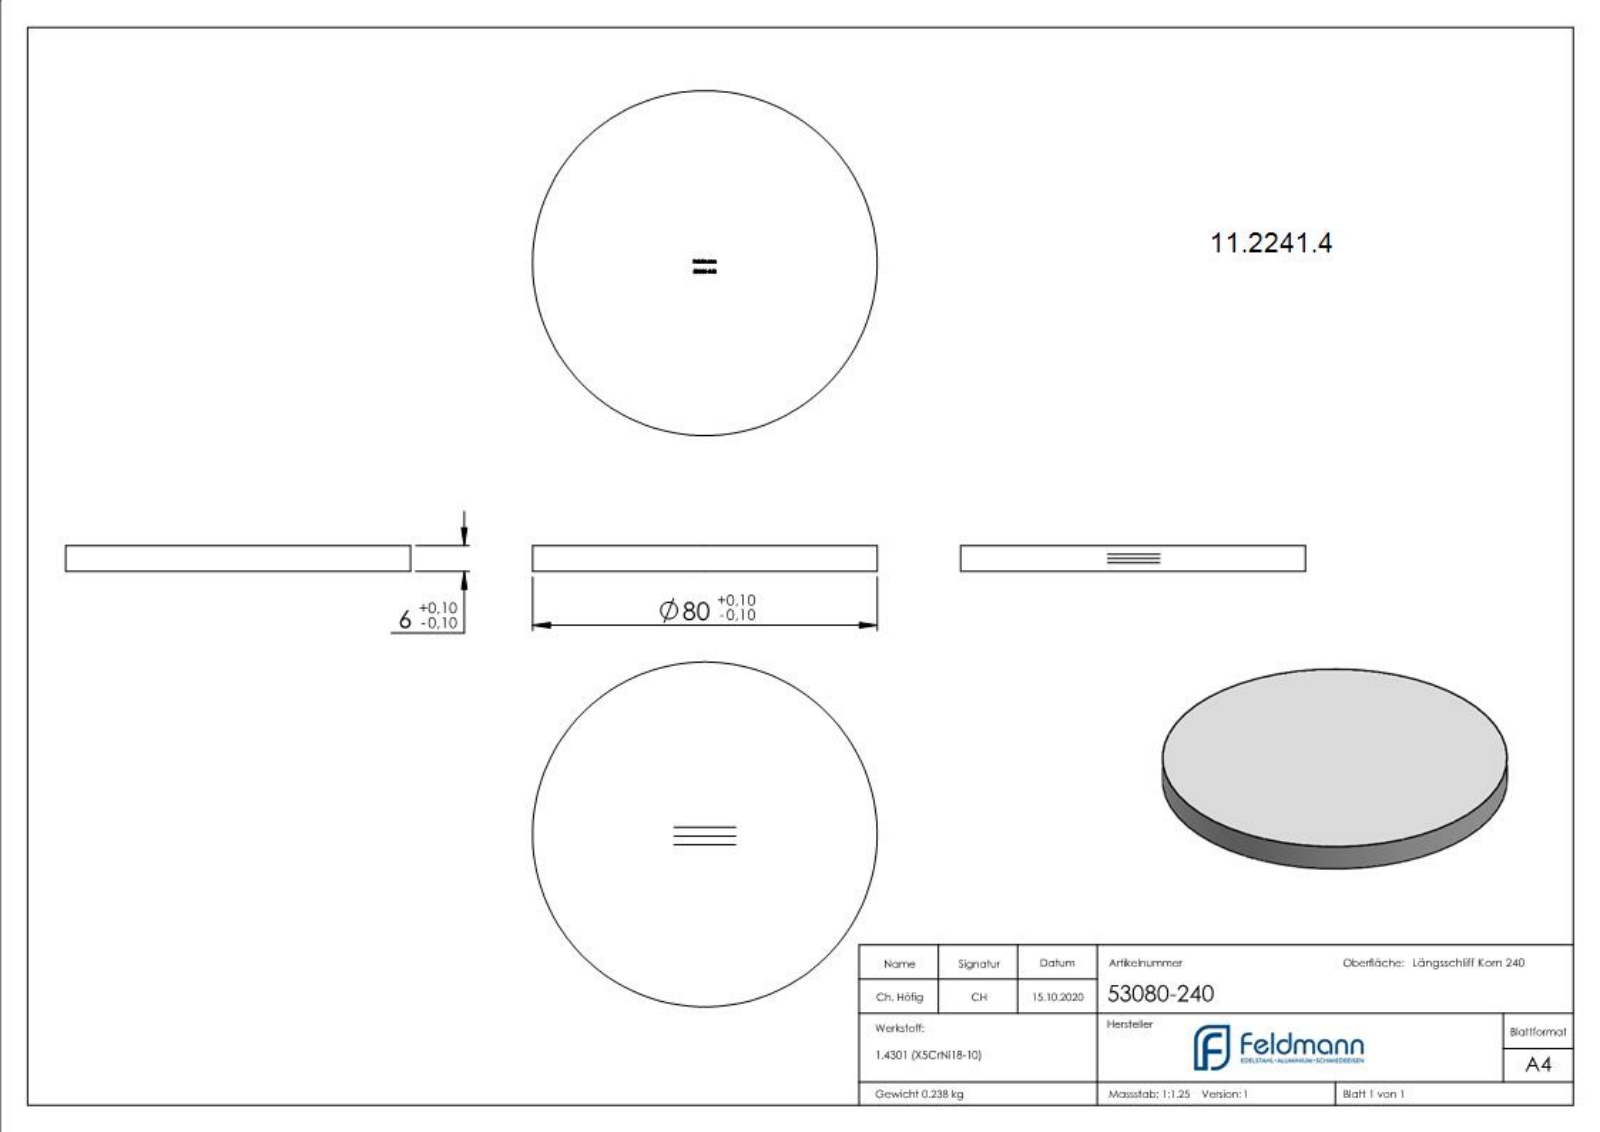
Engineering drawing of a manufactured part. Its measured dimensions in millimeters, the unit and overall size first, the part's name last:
Units: millimetres
Overall size (bounding box): 80 × 80 × 6
Round bosses / shafts (diameter × count): ⌀80 ×1
Main face-to-face distances: 6, 5.9, 1.78, 2.45, 0.83, 2.41, 0.99, 0.4, 2.77, 0.67
Volume: 30 159 mm³ · Surface area: 11 567 mm²
Bodies: 1 solid, 236 faces (114 planar, 2 cylindrical, 120 other)
Part name (STEP PRODUCT): 53080-240
STEP written by: SolidWorks 2018 (CONFIG_CONTROL_DESIGN)
